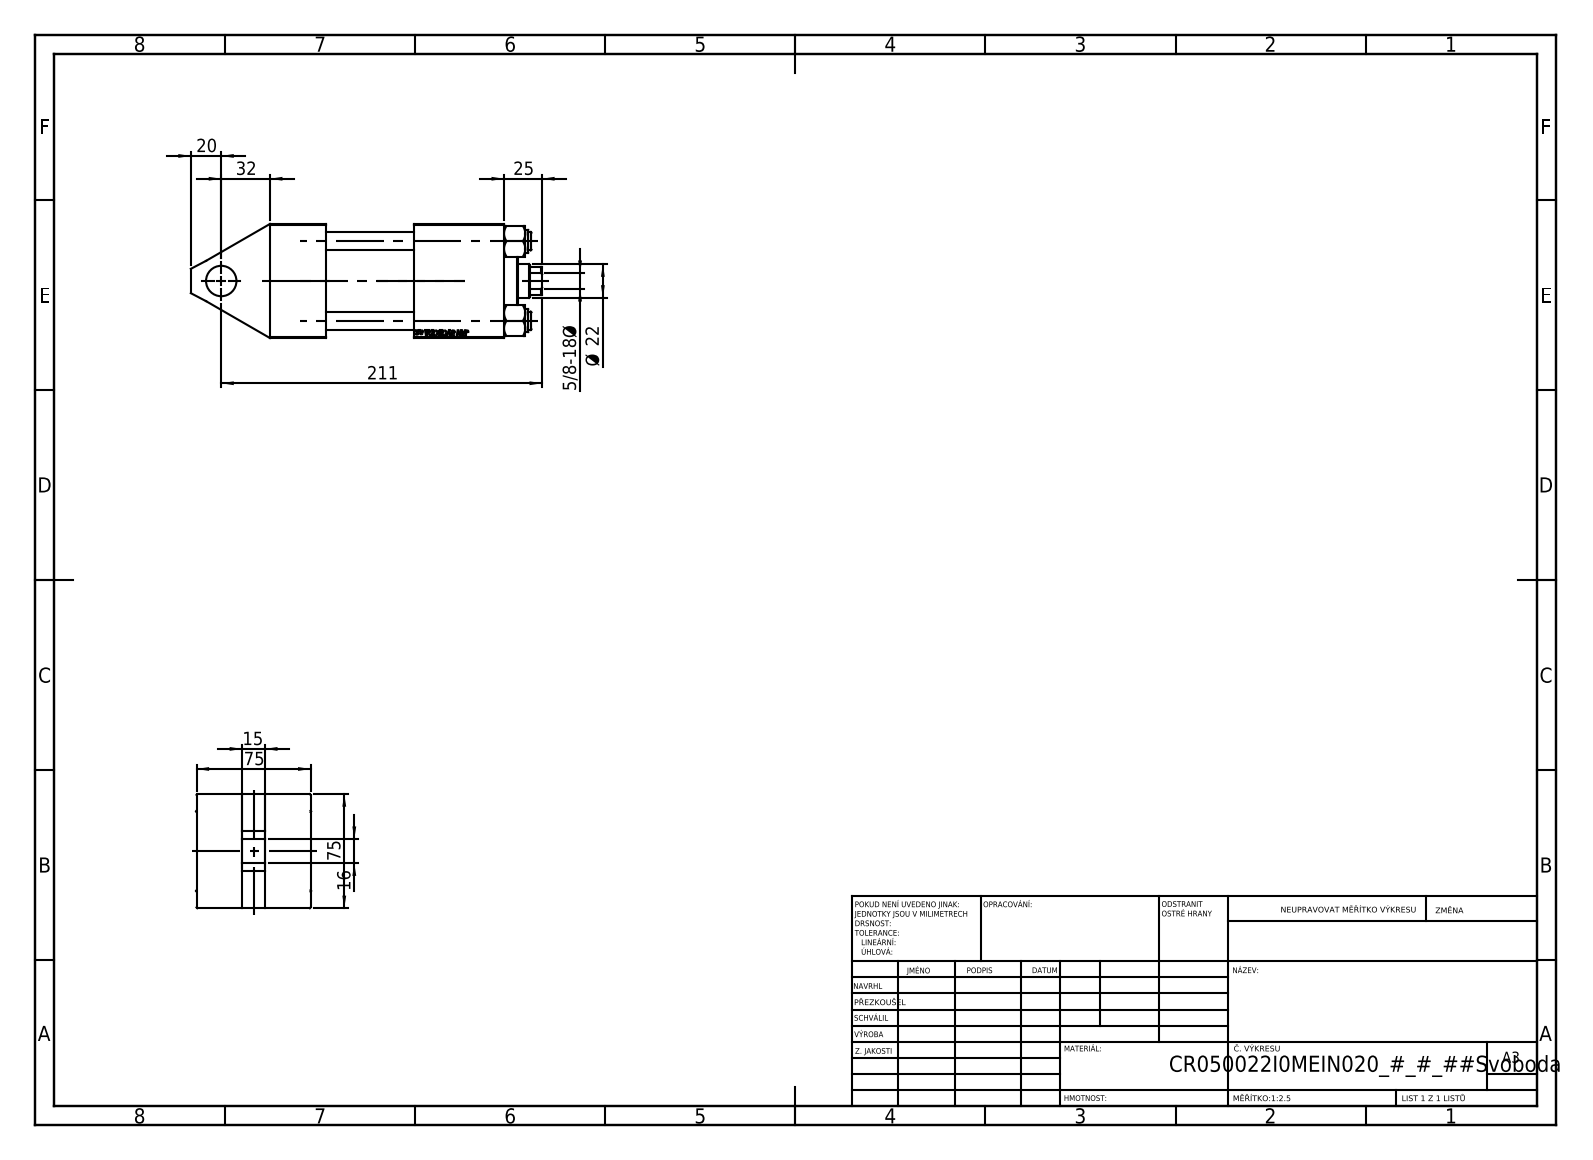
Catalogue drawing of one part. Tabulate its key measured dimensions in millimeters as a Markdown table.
| quantity | value |
| --- | --- |
| part name | V215CR_TYCINKA_I; NUT_M5_I; V215CR_I_Body; V215_VC_A (+1 more) |
| STEP written by | SolidWorks 2019 (CONFIG_CONTROL_DESIGN) |
| units | millimeters |
| bodies | 11 solids, 1078 faces (502 planar, 80 cylindrical, 496 other) |
| overall size | 231 × 75.54 × 75 |
| volume | 700 038 mm³ |
| surface area | 156 181 mm² |
| round holes (diameter × count) | 12 × 4, 7 × 2, 20.96 × 2, 30 × 2, 10.5 × 1, 20 × 1, 22 × 1, 25 × 1, 41 × 1, 50 × 1, 53 × 1 |
| round bosses / shafts (diameter × count) | 15 × 4, 56 × 1, 34 × 1 |
| partial cylindrical surfaces (radius × count) | 10.5 × 1 |
| main face-to-face distances | 75, 117, 37, 154, 45, 30, 95, 58, 59, 125.3 |
| hole center spacings | 36.98, 52.3, 73.96, 93.5 |
